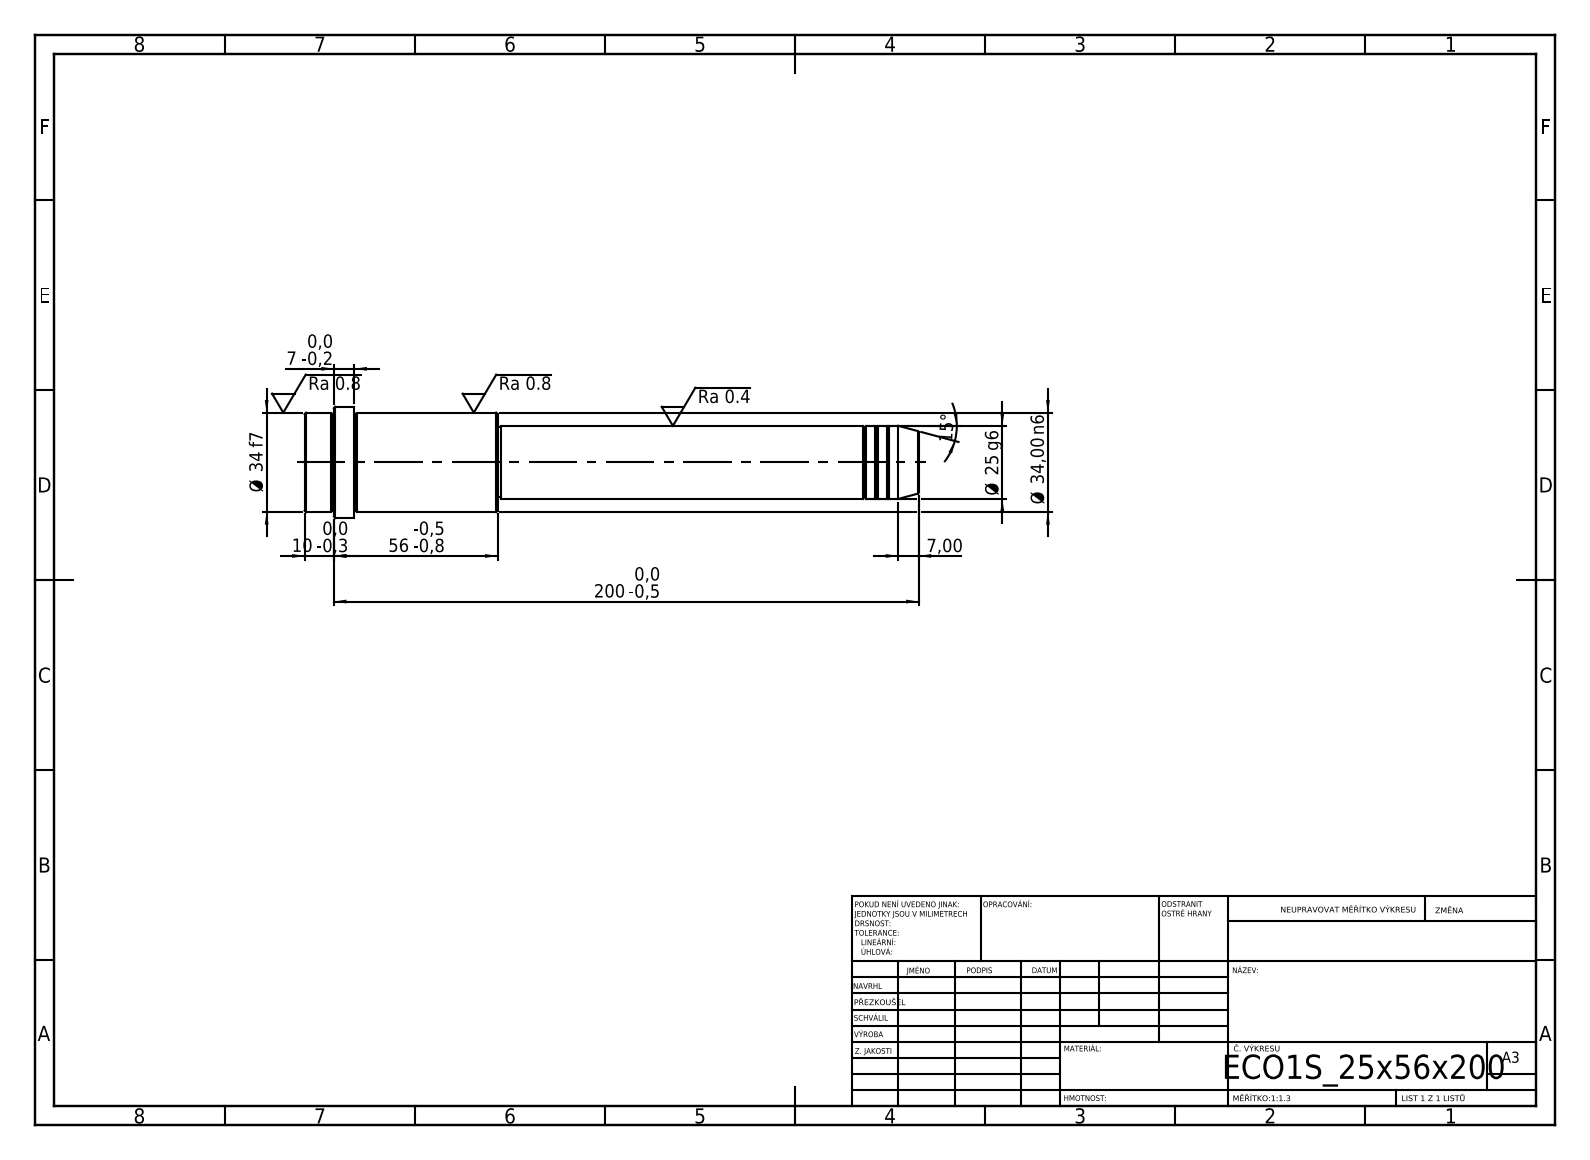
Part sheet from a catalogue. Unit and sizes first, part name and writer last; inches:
Units: inches
Overall size (bounding box): 8.268 × 1.496 × 1.496
Round bosses / shafts (diameter × count): ⌀1.496 ×1, ⌀1.339 ×1, ⌀0.984 ×1, ⌀0.945 ×1
Main face-to-face distances: 2.598, 5.669, 8.268, 7.598, 1.929, 0.669, 7.874, 2.205, 0.276, 0.394
Volume: 8.021 in³ · Surface area: 32.19 in²
Bodies: 1 solid, 52 faces (6 planar, 16 cylindrical, 30 other)
STEP written by: SolidWorks 2019 (CONFIG_CONTROL_DESIGN)
